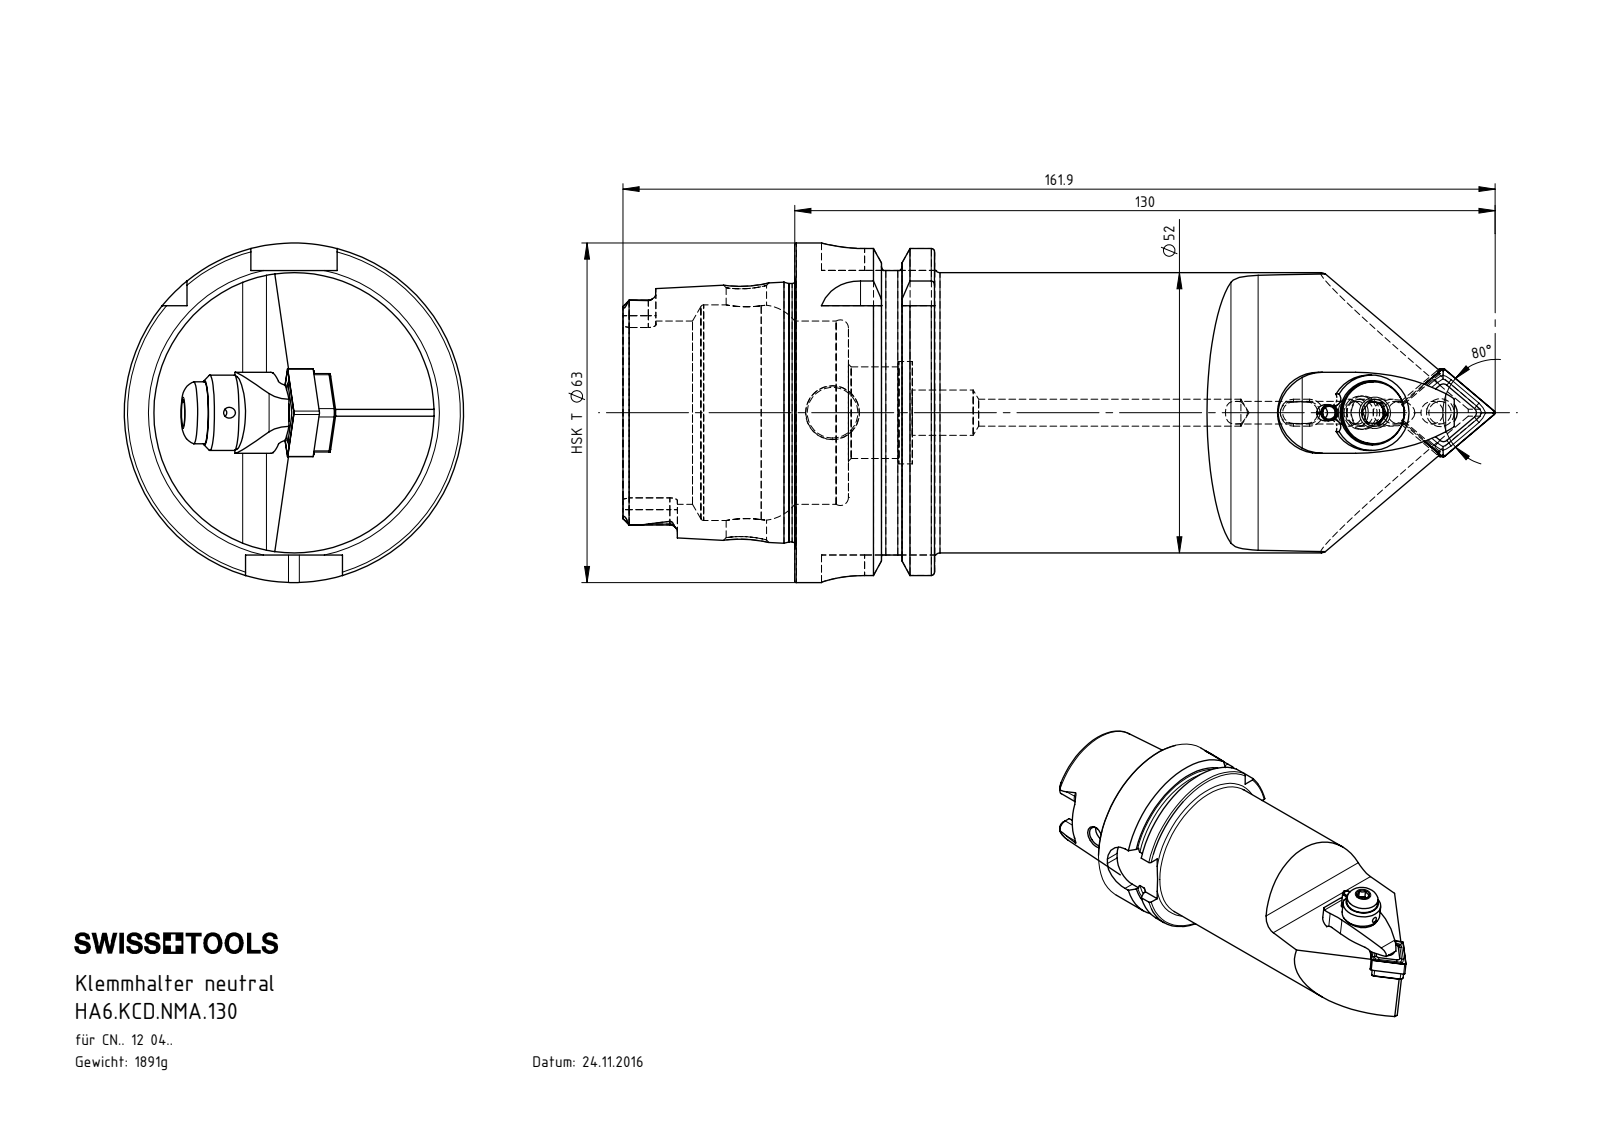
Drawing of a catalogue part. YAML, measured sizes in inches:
part_name: "WCC-ER5.102.005_A; WCD-ER2.101.003_A; WCC-ER2.001.010_A; WCC-ER4.103.032_A (+7 more)"
step_written_by: "SolidWorks 2017 (AUTOMOTIVE_DESIGN)"
units: inches
bodies: {solids: 11, faces: 341, planar: 125, cylindrical: 101, other: 115}
overall_size: [6.374, 2.48, 2.48]
volume: 14.65
surface_area: 65.9
round_holes:
  - {diameter: 0.079, count: 3}
  - {diameter: 0.165, count: 3}
  - {diameter: 0.197, count: 3}
  - {diameter: 0.276, count: 2}
  - {diameter: 0.094, count: 1}
  - {diameter: 0.118, count: 1}
  - {diameter: 0.157, count: 1}
  - {diameter: 0.203, count: 1}
  - {diameter: 0.244, count: 1}
  - {diameter: 0.252, count: 1}
  - {diameter: 0.295, count: 1}
  - {diameter: 0.331, count: 1}
round_bosses_or_shafts:
  - {diameter: 0.197, count: 2}
  - {diameter: 0.118, count: 2}
  - {diameter: 2.48, count: 1}
  - {diameter: 2.163, count: 1}
  - {diameter: 2.047, count: 1}
  - {diameter: 1.887, count: 1}
  - {diameter: 0.551, count: 1}
  - {diameter: 0.453, count: 1}
partial_cylinders:
  - {radius: 0.015, count: 6}
  - {radius: 0.055, count: 6}
  - {radius: 0.016, count: 4}
  - {radius: 0.039, count: 4}
  - {radius: 0.315, count: 4}
  - {radius: 0.027, count: 3}
  - {radius: 0.027, count: 3}
  - {radius: 0.059, count: 3}
face_to_face_distances: [1.022, 0.63, 0.392, 1.256, 1.648, 2.278, 2.079, 0.858, 0.467, 0.176]
hole_center_spacings: [0.315, 0.263, 0.323, 0.578, 0.591, 0.605, 0.906, 0.92]
